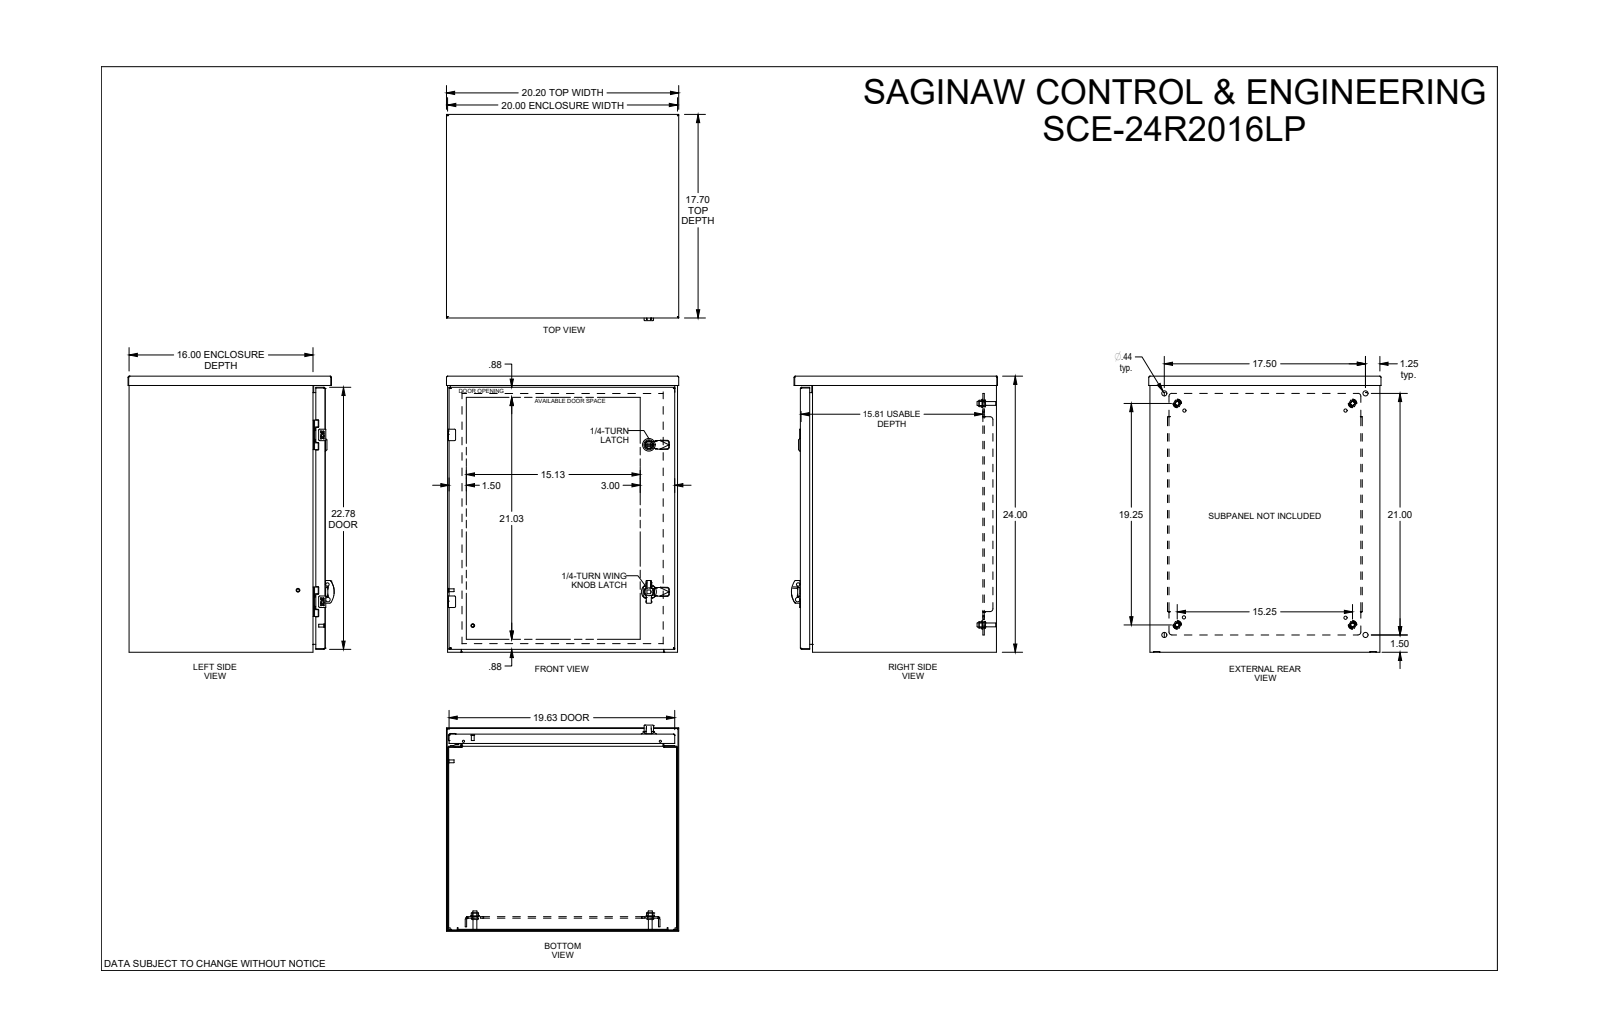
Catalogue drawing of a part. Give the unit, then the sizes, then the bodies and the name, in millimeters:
Units: millimetres
Overall size (bounding box): 609.6 × 513.1 × 455.3
Round holes (diameter × count): ⌀4.4 ×4, ⌀5.2 ×4, ⌀6.2 ×4, ⌀6.8 ×4, ⌀7.1 ×4, ⌀9.3 ×4, ⌀9.5 ×4, ⌀11.1 ×4, ⌀12.7 ×4, ⌀1 ×2, ⌀4 ×2, ⌀4.8 ×2
Round bosses / shafts (diameter × count): ⌀4.3 ×6, ⌀9.3 ×4, ⌀8.4 ×4, ⌀6.4 ×4, ⌀6.1 ×4, ⌀5 ×3, ⌀22 ×2, ⌀20.4 ×2
Partial cylindrical surfaces — rounded edges, fillets, slot ends (radius × count): R0.4 ×72, R0.3 ×60, R0.3 ×26, R0.5 ×24, R2.8 ×21, R1.3 ×19, R0.8 ×15, R0.8 ×12
Main face-to-face distances: 1.5, 506.5, 608.1, 1.5, 430.1, 431.6, 433.1, 431.6, 3.2, 508
Hole centre spacings: 368.3, 0.6, 12.5, 25, 416.5, 22.2, 58.3, 372
Bodies: 0 solids, 2365 faces (1132 planar, 799 cylindrical, 434 other)
Part name (STEP PRODUCT): SCE-24R2016LP
STEP written by: SolidWorks 2019 (CONFIG_CONTROL_DESIGN)
